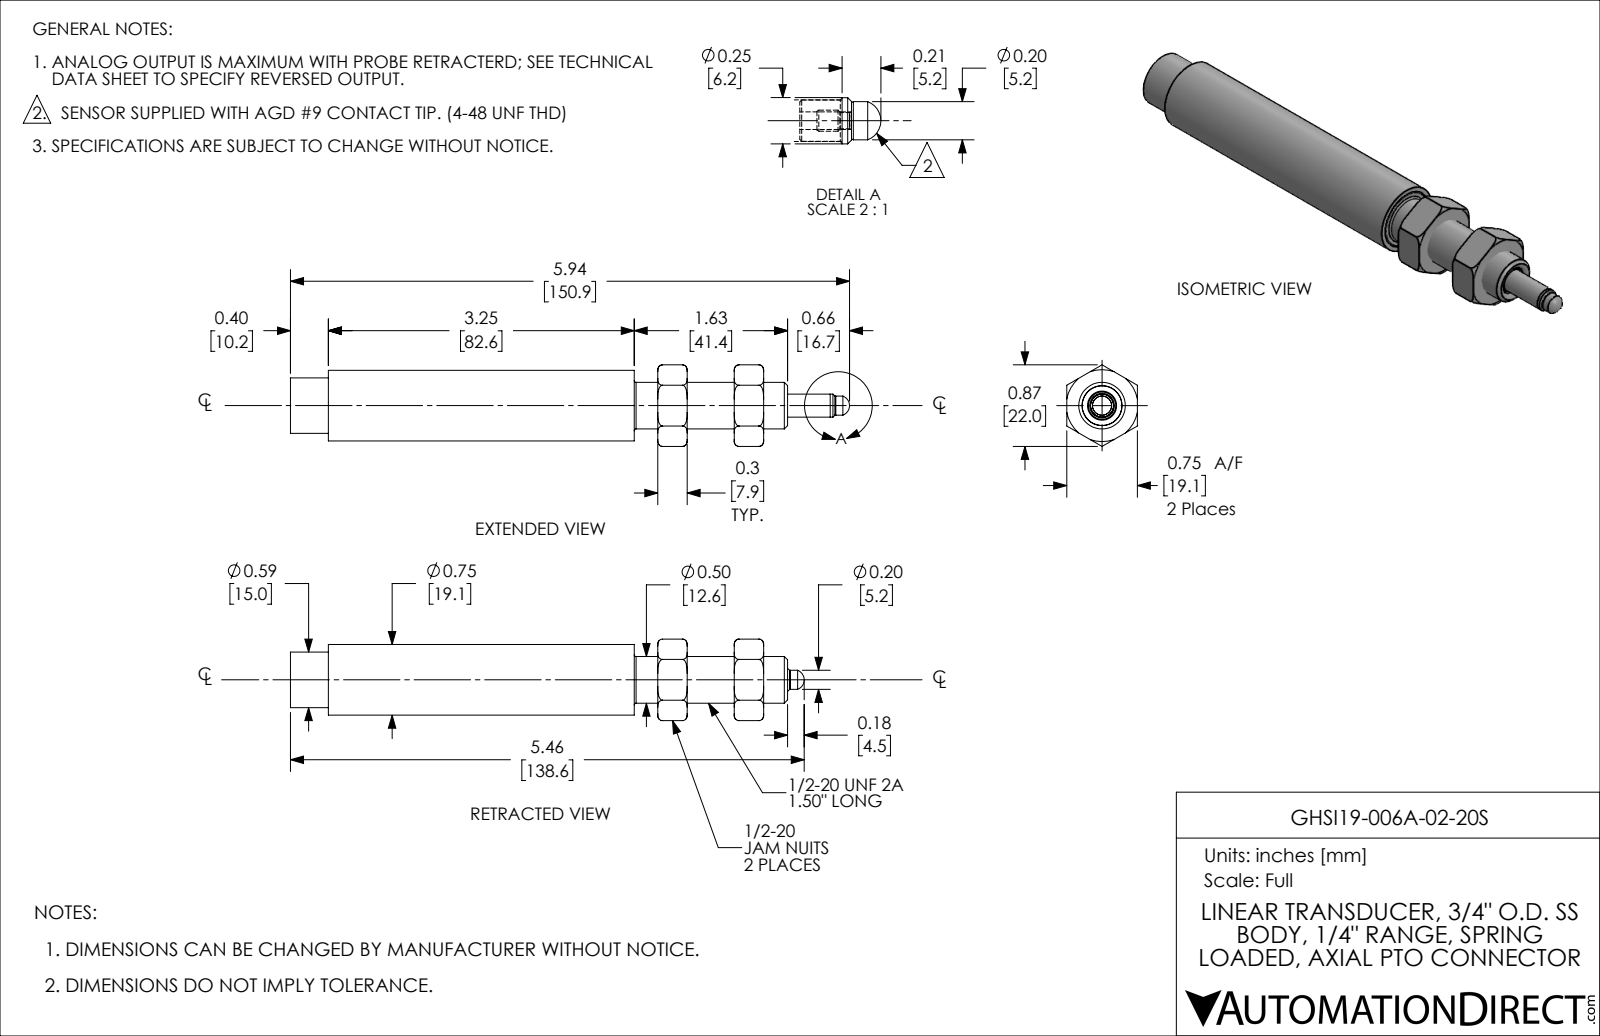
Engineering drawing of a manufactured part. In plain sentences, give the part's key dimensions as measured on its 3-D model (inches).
The part is named "GHSI19-006A-02-20S". Its 3-D file was written by "SolidWorks 2019 (AUTOMOTIVE_DESIGN)". It is 11 solids with 187 faces: 77 planar, 65 cylindrical and 45 other. Overall it measures 5.458 by 0.866 by 0.75 inches. Its volume is 1.155 cubic inches and its surface area 35.19 square inches. Round holes: 1 of diameter 0.093, 1 of diameter 0.156, 1 of diameter 0.193, 1 of diameter 0.221, 1 of diameter 0.249, 1 of diameter 0.302, 1 of diameter 0.31, 1 of diameter 0.453, 1 of diameter 0.52, 1 of diameter 0.62, 1 of diameter 0.625, 1 of diameter 0.65. Round bosses or shafts: 6 of diameter 0.03, 1 of diameter 0.75, 1 of diameter 0.725, 1 of diameter 0.672, 1 of diameter 0.624, 1 of diameter 0.59, 1 of diameter 0.495, 1 of diameter 0.375. Partial cylindrical surfaces (rounded edges, fillets, slot ends): 2 of radius 0.011, 2 of radius 0.04, 1 of radius 0.133, 1 of radius 0.156, 1 of radius 0.275. The main face-to-face distances are 0.75, 0.812, 0.313, 0.813, 1.125, 0.5, 0.312, 0.75, 3.522, 3.835.
